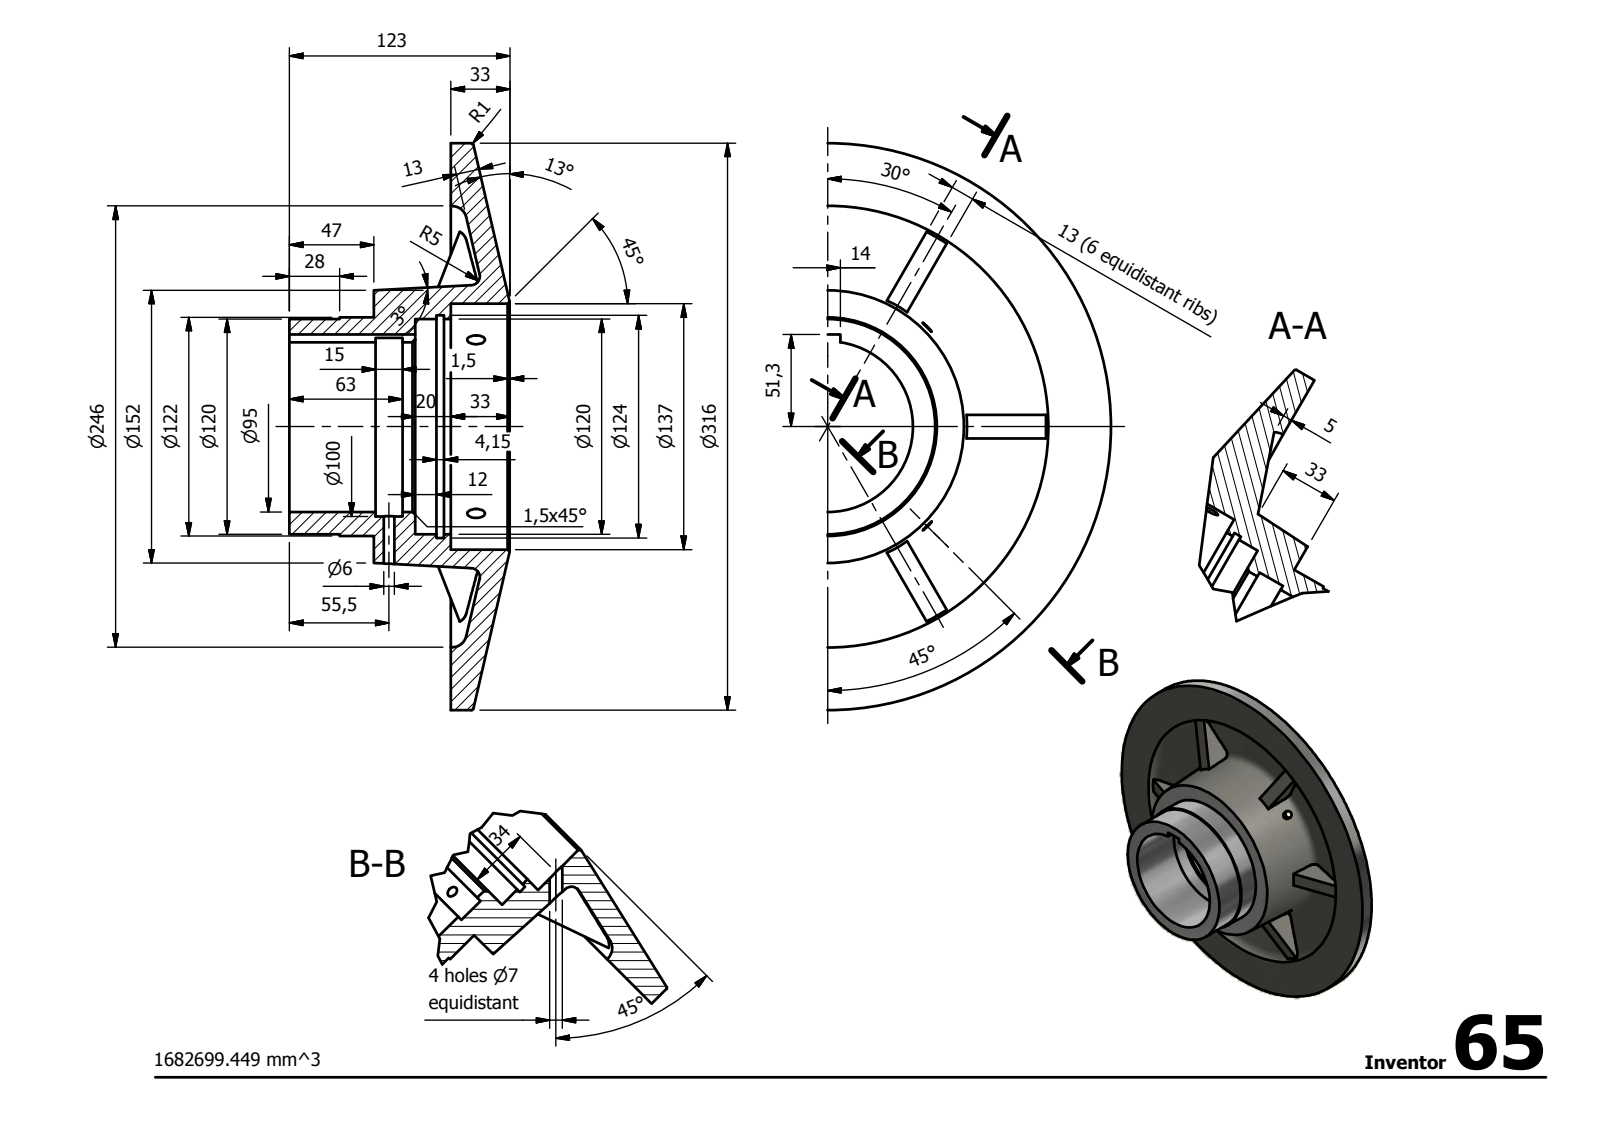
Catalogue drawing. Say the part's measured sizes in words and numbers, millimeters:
Its 3-D file was written by "Autodesk Inventor 2014 (AUTOMOTIVE_DESIGN)". It is 1 solid with 65 faces: 31 planar, 16 cylindrical and 18 other. Overall it measures 316 by 316 by 122.72 millimeters. Its volume is 1 683 000 cubic millimeters and its surface area 257 838 square millimeters. Round holes: 4 of diameter 7, 1 of diameter 6, 1 of diameter 95, 1 of diameter 100, 1 of diameter 120, 1 of diameter 124, 1 of diameter 137, 1 of diameter 246. Round bosses or shafts: 1 of diameter 316, 1 of diameter 122. The main face-to-face distances are 43, 47, 90, 20, 13, 70, 23, 35, 19, 42.
